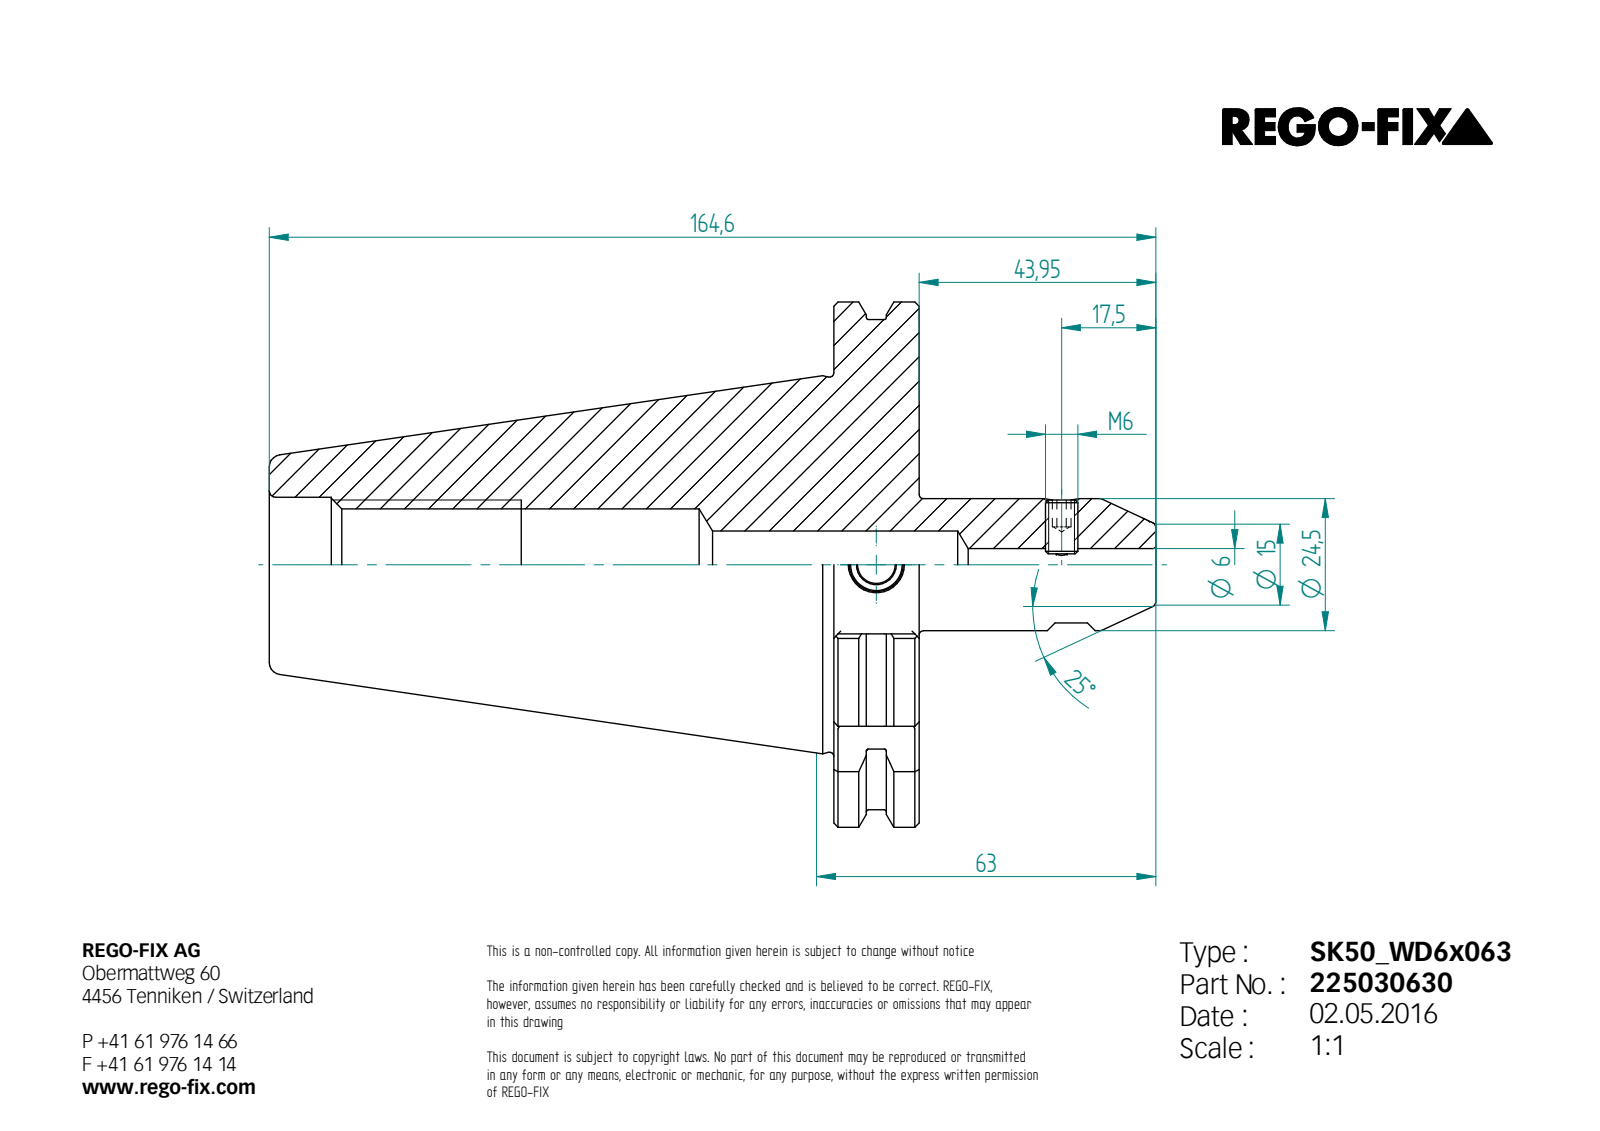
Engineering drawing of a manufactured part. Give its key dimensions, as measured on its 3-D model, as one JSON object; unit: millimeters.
{"step_written_by": "Unknown (AUTOMOTIVE_DESIGN)", "units": "millimeters", "bodies": {"solids": 2, "faces": 121, "planar": 58, "cylindrical": 24, "other": 39}, "overall_size": [164.6, 97.5, 93.58], "volume_mm3": 346312, "surface_area_mm2": 46801, "round_holes": [[4.92, 1], [6, 1], [7, 1], [10, 1], [12.5, 1], [20.75, 1], [25, 1]], "round_bosses_or_shafts": [[91, 1], [24.5, 1], [6, 1]], "partial_cylinders_radius": [[0.5, 5], [48.75, 1]], "face_to_face_distances": [15.85, 104.8, 120.65, 72.8, 25.7, 164.6, 59.8, 43.95, 114.57, 9.77]}
